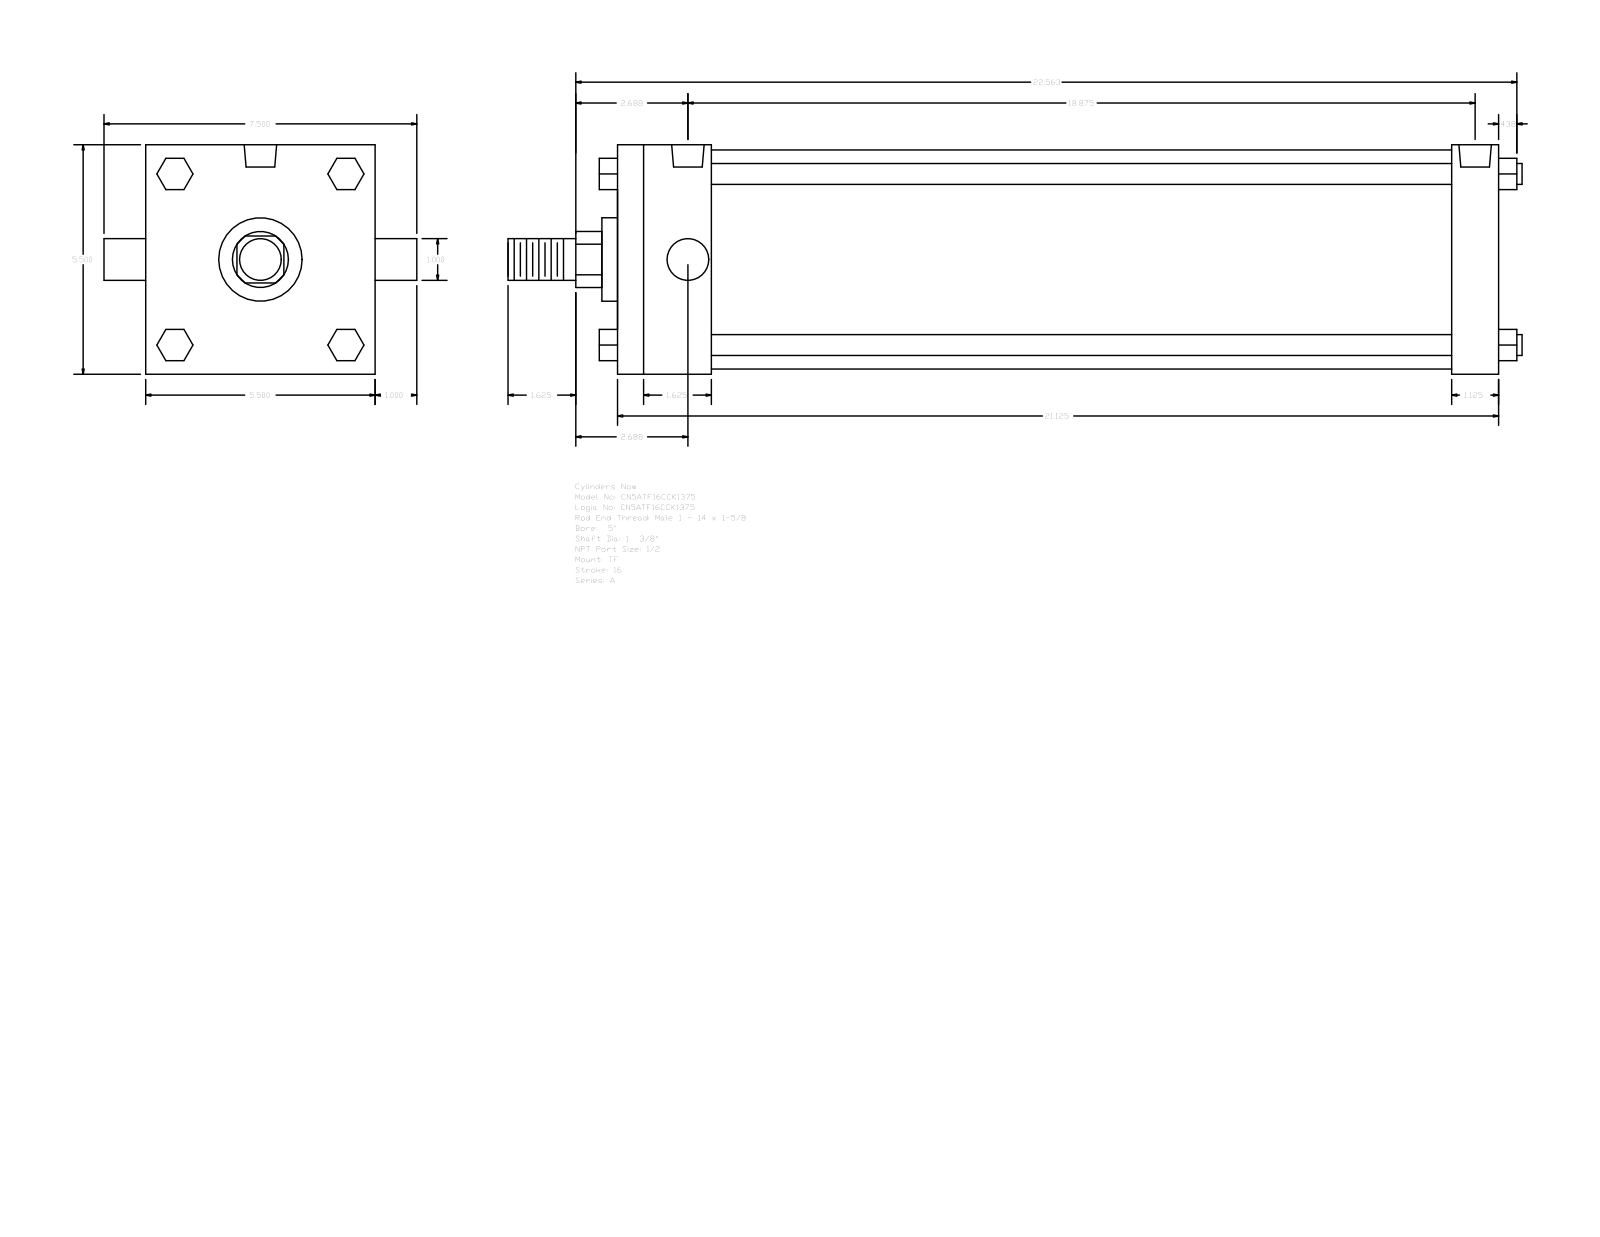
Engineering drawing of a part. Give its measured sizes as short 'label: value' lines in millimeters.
name: A_TF__0500_1.375
written by: GSSL Pune (CONFIG_CONTROL_DESIGN)
unit: mm
bodies: 0 solids, 120 faces (92 planar, 28 cylindrical, 0 other)
size: 617.54 × 190.5 × 139.7
holes: 3× ⌀8.73, 2× ⌀19.77
bosses: 4× ⌀12.7, 2× ⌀25.4, 1× ⌀133.35, 1× ⌀50.8, 1× ⌀34.92
rounds: 1× R17.06
face distances: 139.7, 536.58, 57.15, 28.58, 508, 450.85, 479.43, 19.05, 52.07, 90.18
hole spacings: 2.39, 477.04, 474.65, 479.43
